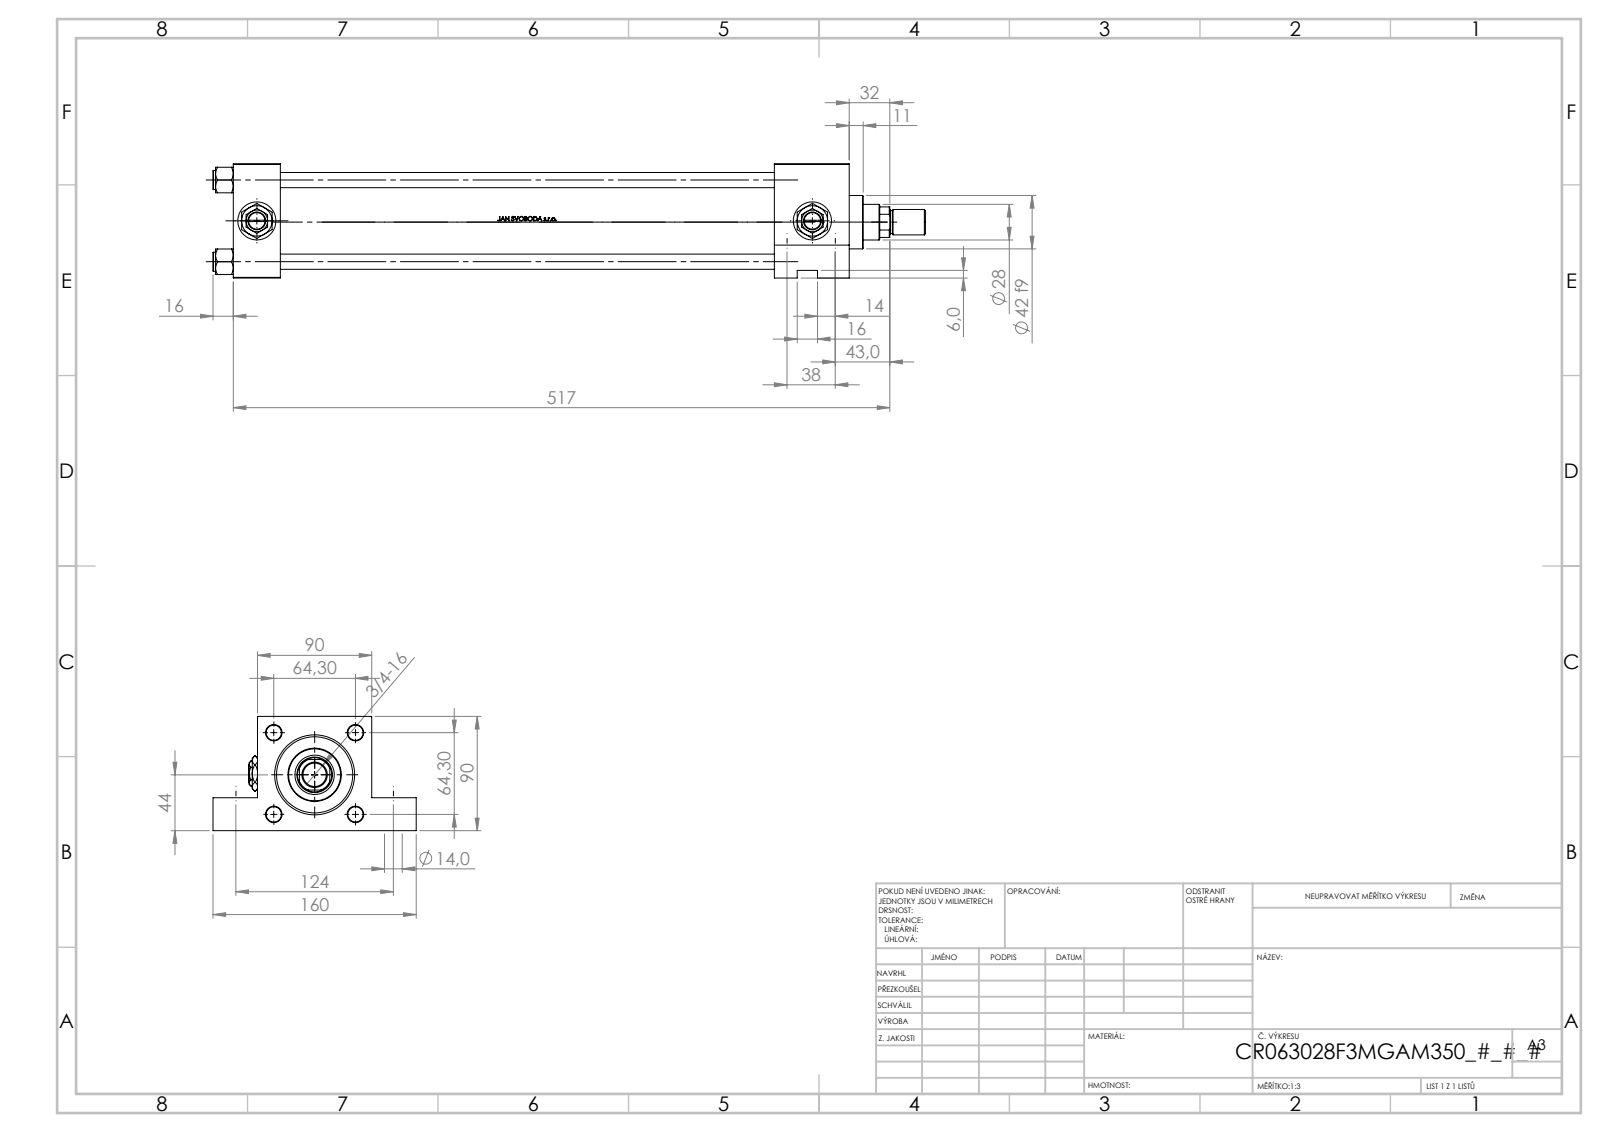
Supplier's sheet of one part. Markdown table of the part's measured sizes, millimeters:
| quantity | value |
| --- | --- |
| part name | V215CR_F_TYCINKA; NUT_M5_F; V215CR_F_Body; Zatka_pro_OIL_PORT (+3 more) |
| STEP written by | SolidWorks 2019 (CONFIG_CONTROL_DESIGN) |
| units | millimeters |
| bodies | 14 solids, 1231 faces (492 planar, 151 cylindrical, 588 other) |
| overall size | 561 × 160 × 90 |
| volume | 1 579 000 mm³ |
| surface area | 417 089 mm² |
| round holes (diameter × count) | 12 × 4, 18 × 4, 20.96 × 4, 30 × 4, 7 × 3, 2.5 × 2, 18.5 × 1, 28 × 1, 31 × 1, 50 × 1, 60 × 1, 63 × 1 |
| round bosses / shafts (diameter × count) | 15 × 4, 69 × 1, 42 × 1, 20 × 1, 18 × 1 |
| partial cylindrical surfaces (radius × count) | 13.5 × 1 |
| main face-to-face distances | 90, 37, 485, 448, 426, 389, 59, 64, 26, 456.3 |
| hole center spacings | 32.39, 45.47, 64.3, 68.42, 28.25, 38, 62.72, 68.24 |
